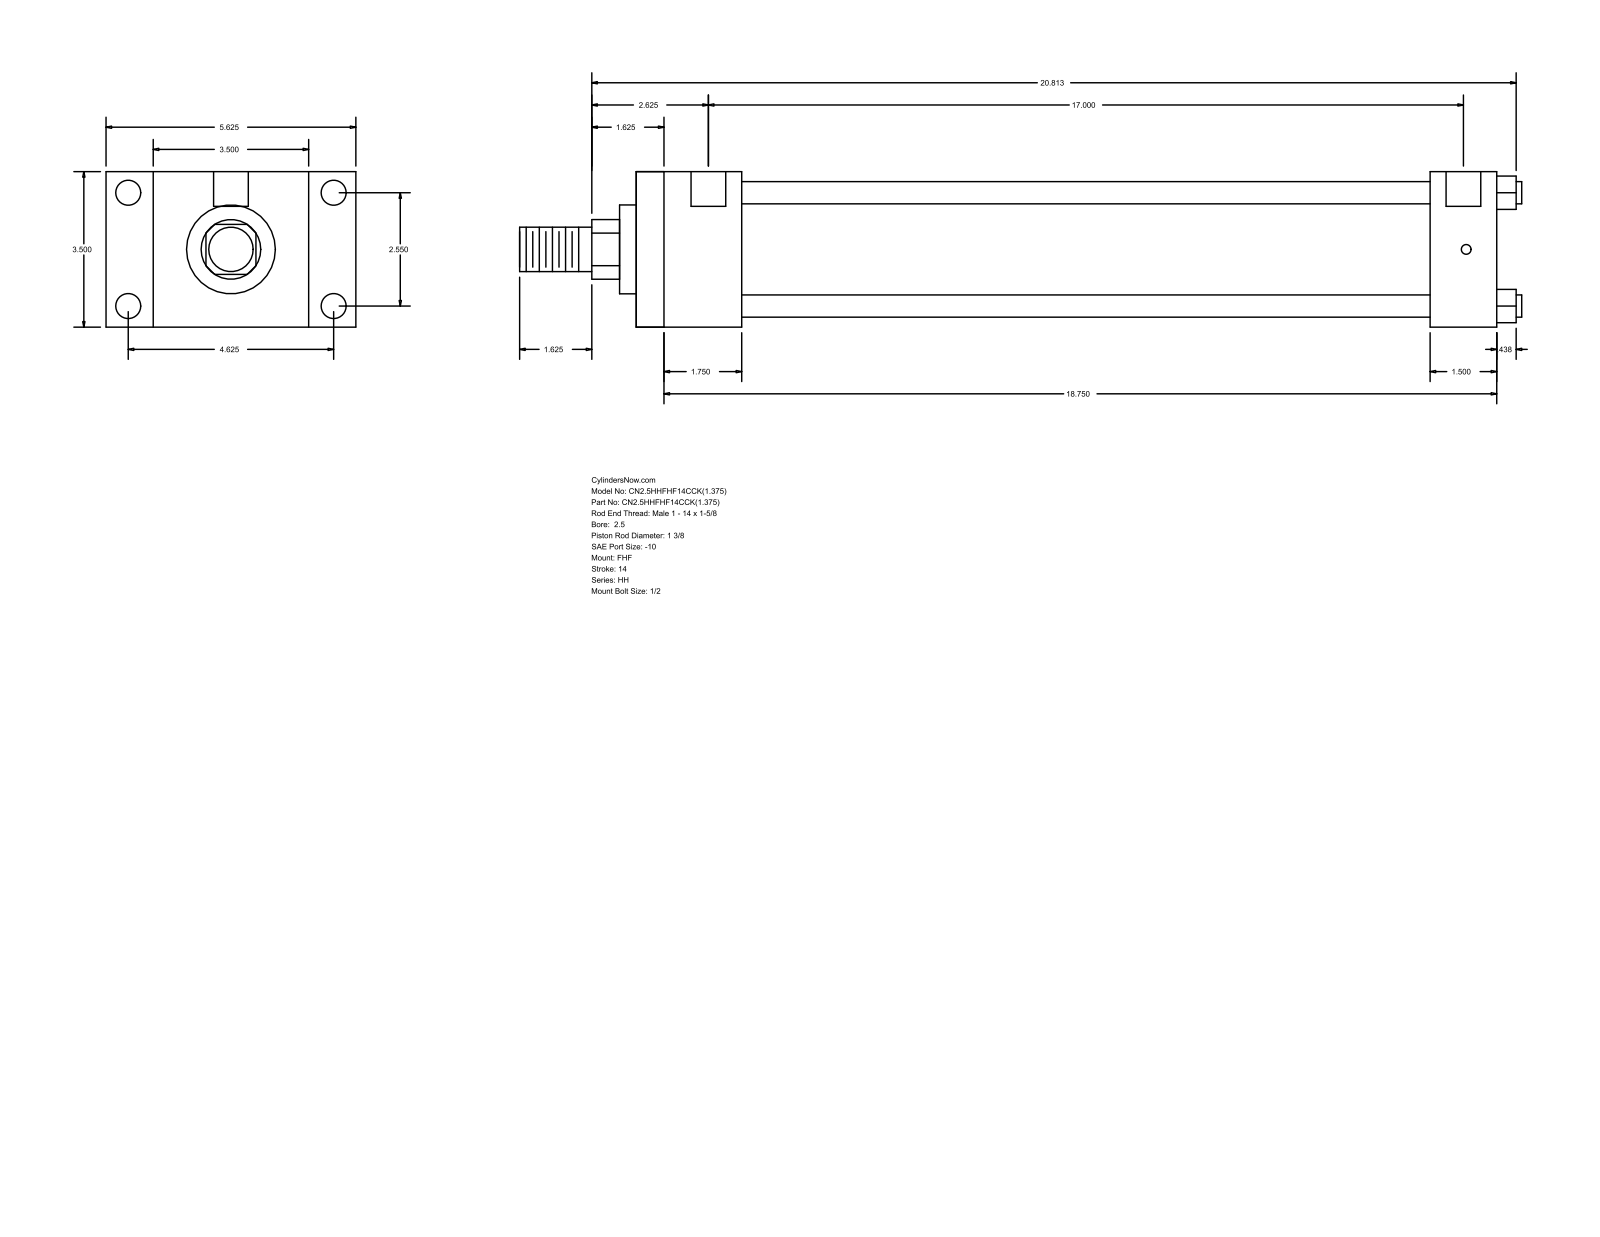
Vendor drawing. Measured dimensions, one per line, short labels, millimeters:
name: HH_FHF__0250_1.375
written by: GSSL Pune (CONFIG_CONTROL_DESIGN)
unit: mm
bodies: 0 solids, 88 faces (60 planar, 28 cylindrical, 0 other)
size: 573.09 × 142.88 × 88.9
holes: 4× ⌀5.56, 4× ⌀14.3, 2× ⌀19.84
bosses: 4× ⌀12.7, 1× ⌀73.03, 1× ⌀50.8, 1× ⌀34.92, 1× ⌀25.4
rounds: 1× R17.06
face distances: 88.9, 60.32, 26.99, 115.89, 492.12, 431.8, 142.88, 454.03, 393.71, 38.09
hole spacings: 1.58, 64.76, 117.48, 134.15, 433.39, 434.97, 431.81
